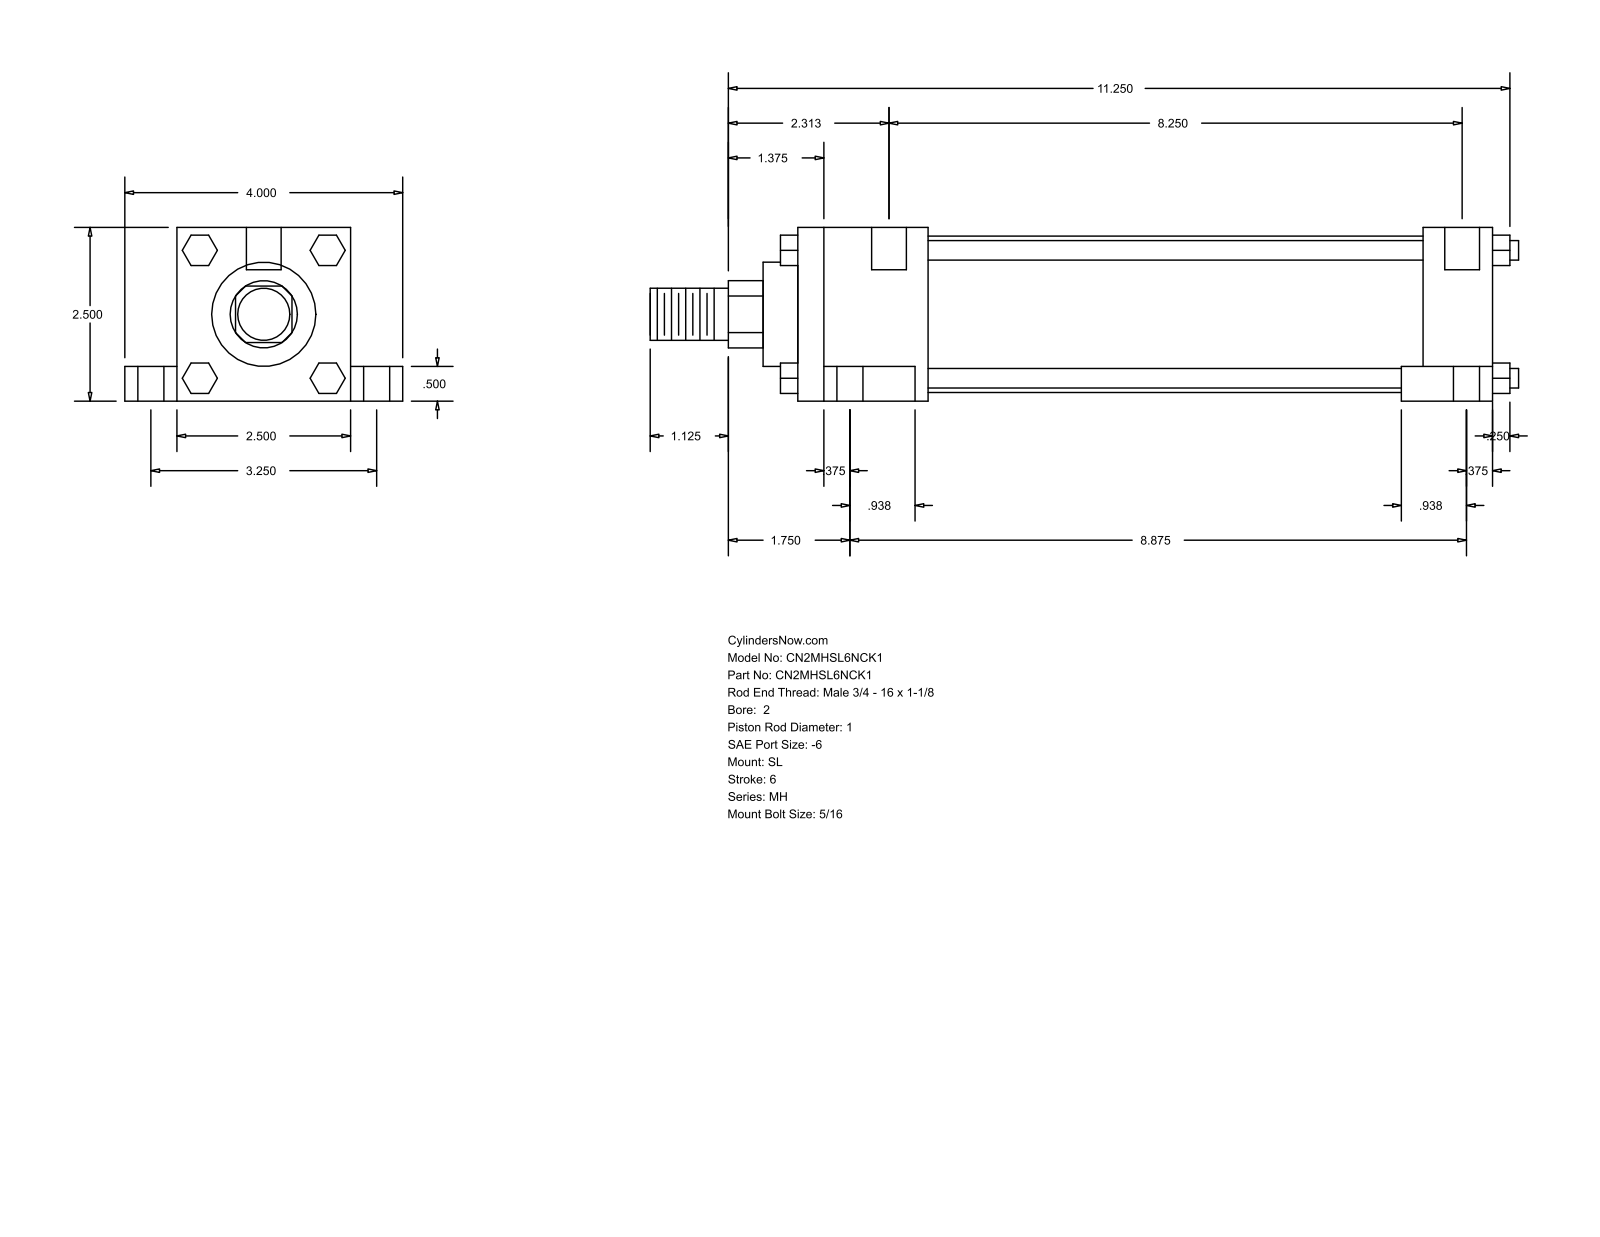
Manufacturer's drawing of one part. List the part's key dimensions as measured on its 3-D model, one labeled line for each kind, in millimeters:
Part name (STEP PRODUCT): MH_SL__0200_1
STEP written by: GSSL Pune (CONFIG_CONTROL_DESIGN)
Units: millimetres
Bodies: 0 solids, 148 faces (112 planar, 36 cylindrical, 0 other)
Overall size (bounding box): 317.5 × 101.6 × 63.5
Round holes (diameter × count): ⌀5.56 ×4, ⌀9.53 ×4, ⌀15.88 ×4, ⌀12.7 ×2
Round bosses / shafts (diameter × count): ⌀7.14 ×4, ⌀57.15 ×1, ⌀38.1 ×1, ⌀25.4 ×1, ⌀19.05 ×1
Partial cylindrical surfaces — rounded edges, fillets, slot ends (radius × count): R12.29 ×1
Main face-to-face distances: 63.5, 254, 12.7, 19.05, 50.8, 82.55, 25.4, 228.6, 47.63, 180.97
Hole centre spacings: 41.3, 42.36, 43.67, 82.54, 215.14, 217.48, 219.81, 225.43
